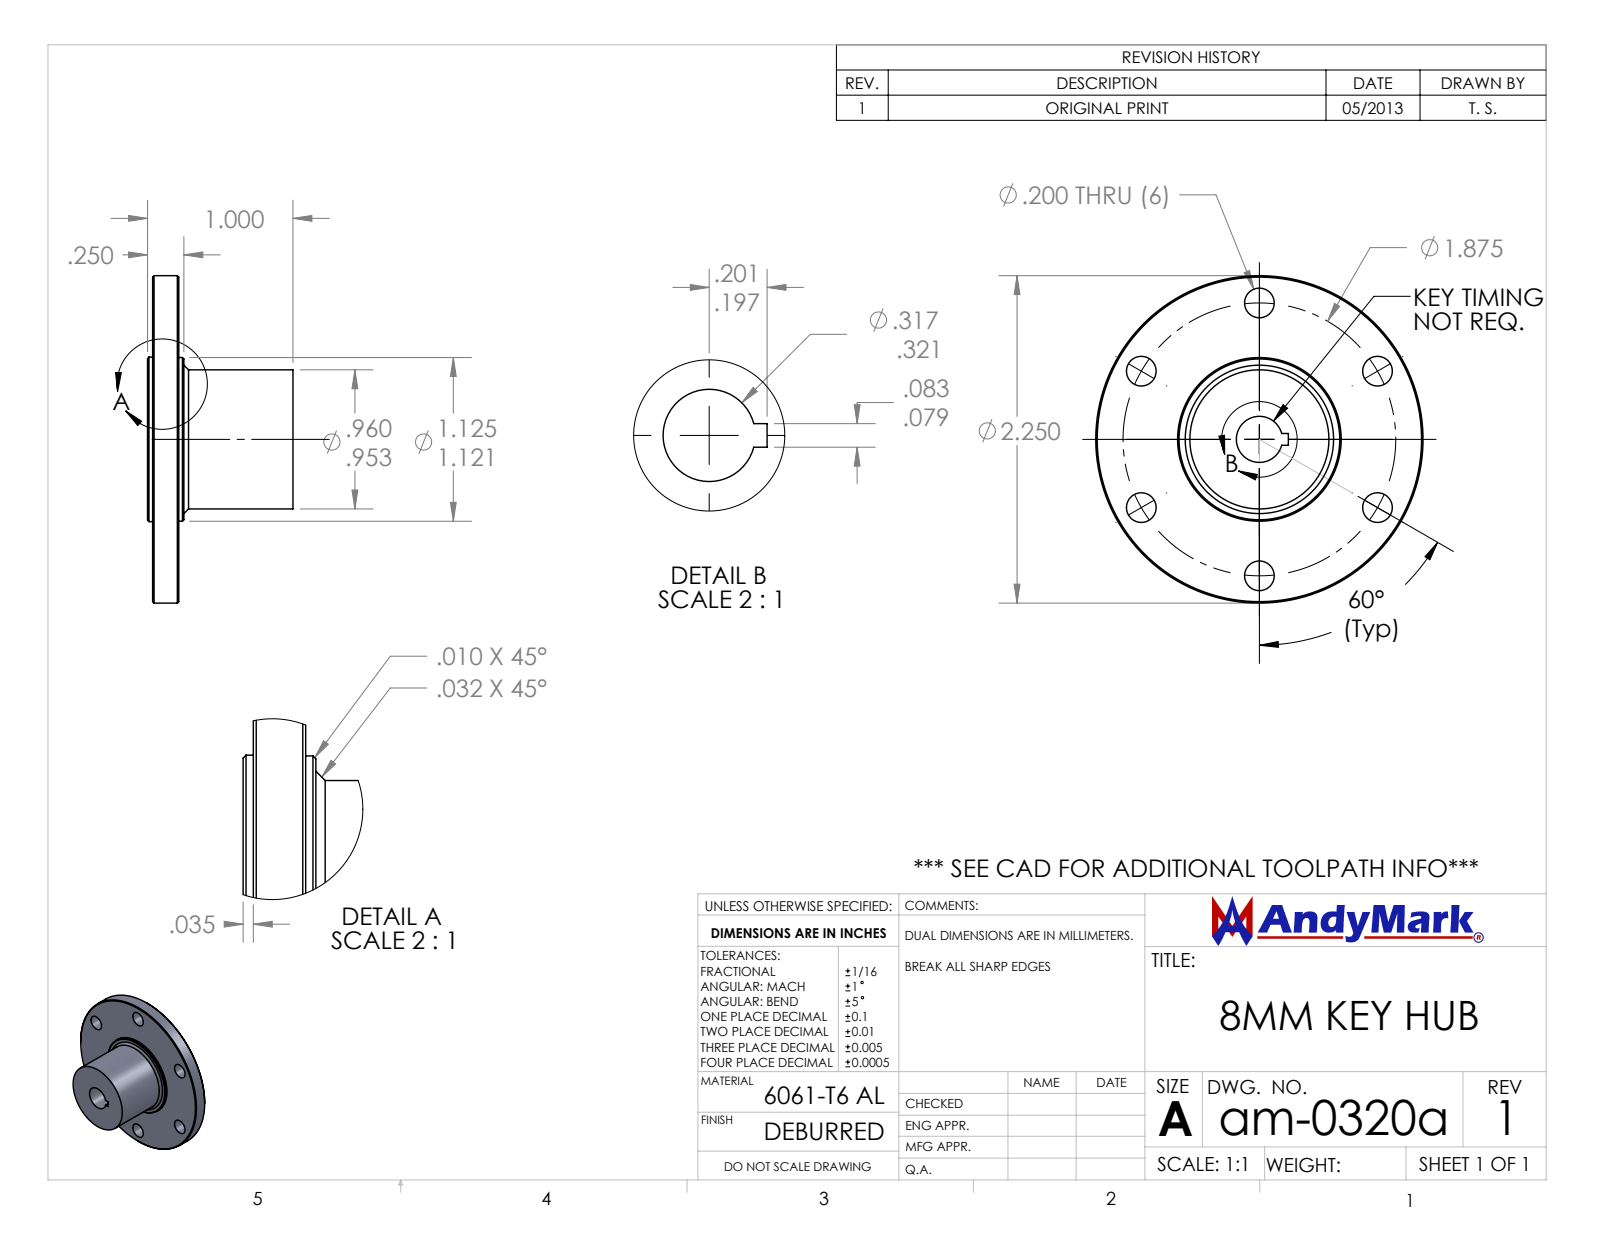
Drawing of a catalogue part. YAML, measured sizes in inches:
part_name: "am-0320a 8mm Key Hub"
step_written_by: "SolidWorks 2014 (AUTOMOTIVE_DESIGN)"
units: inches
bodies: {solids: 1, faces: 39, planar: 8, cylindrical: 21, other: 10}
overall_size: [2.25, 2.25, 1]
volume: 1.207
surface_area: 12.77
round_holes:
  - {diameter: 0.204, count: 6}
  - {diameter: 0.317, count: 1}
round_bosses_or_shafts:
  - {diameter: 2.25, count: 1}
  - {diameter: 1.13, count: 1}
  - {diameter: 1.125, count: 1}
  - {diameter: 0.956, count: 1}
face_to_face_distances: [0.18, 0.035, 0.215, 1, 0.965, 0.785, 0.25, 0.75, 0.081]
hole_center_spacings: [0.937, 1.624, 1.875, 0.938]
